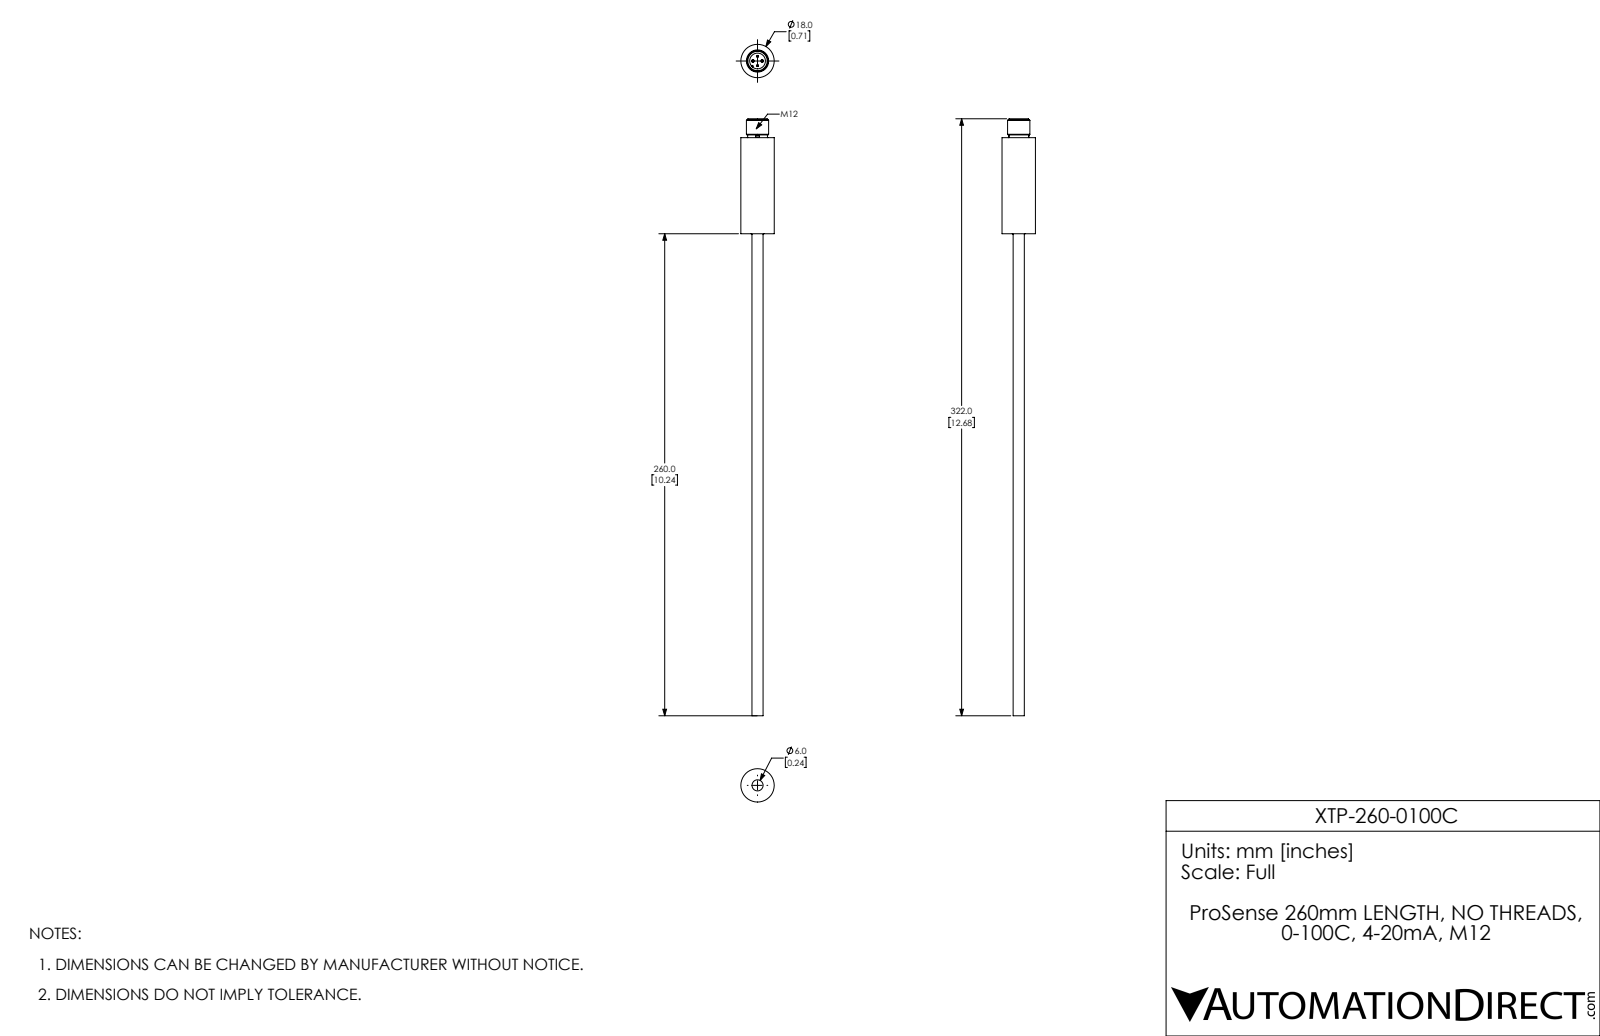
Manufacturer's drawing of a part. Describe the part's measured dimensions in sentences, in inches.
The part is named "XTP-260-0100C". Its 3-D file was written by "SolidWorks 2017 (AUTOMOTIVE_DESIGN)". It is 1 solid with 67 faces: 24 planar, 21 cylindrical and 22 other. Overall it measures 12.677 by 0.709 by 0.709 inches. Its volume is 1.29 cubic inches and its surface area 14.01 square inches. Round holes: 1 of diameter 0.335. Round bosses or shafts: 4 of diameter 0.04, 1 of diameter 0.709, 1 of diameter 0.472, 1 of diameter 0.421, 1 of diameter 0.413, 1 of diameter 0.236. Partial cylindrical surfaces (rounded edges, fillets, slot ends): 1 of radius 0.016. The main face-to-face distances are 2.039, 2.087, 0.047, 2.441, 0.402, 0.354, 10.236, 12.276, 12.323, 12.677.
